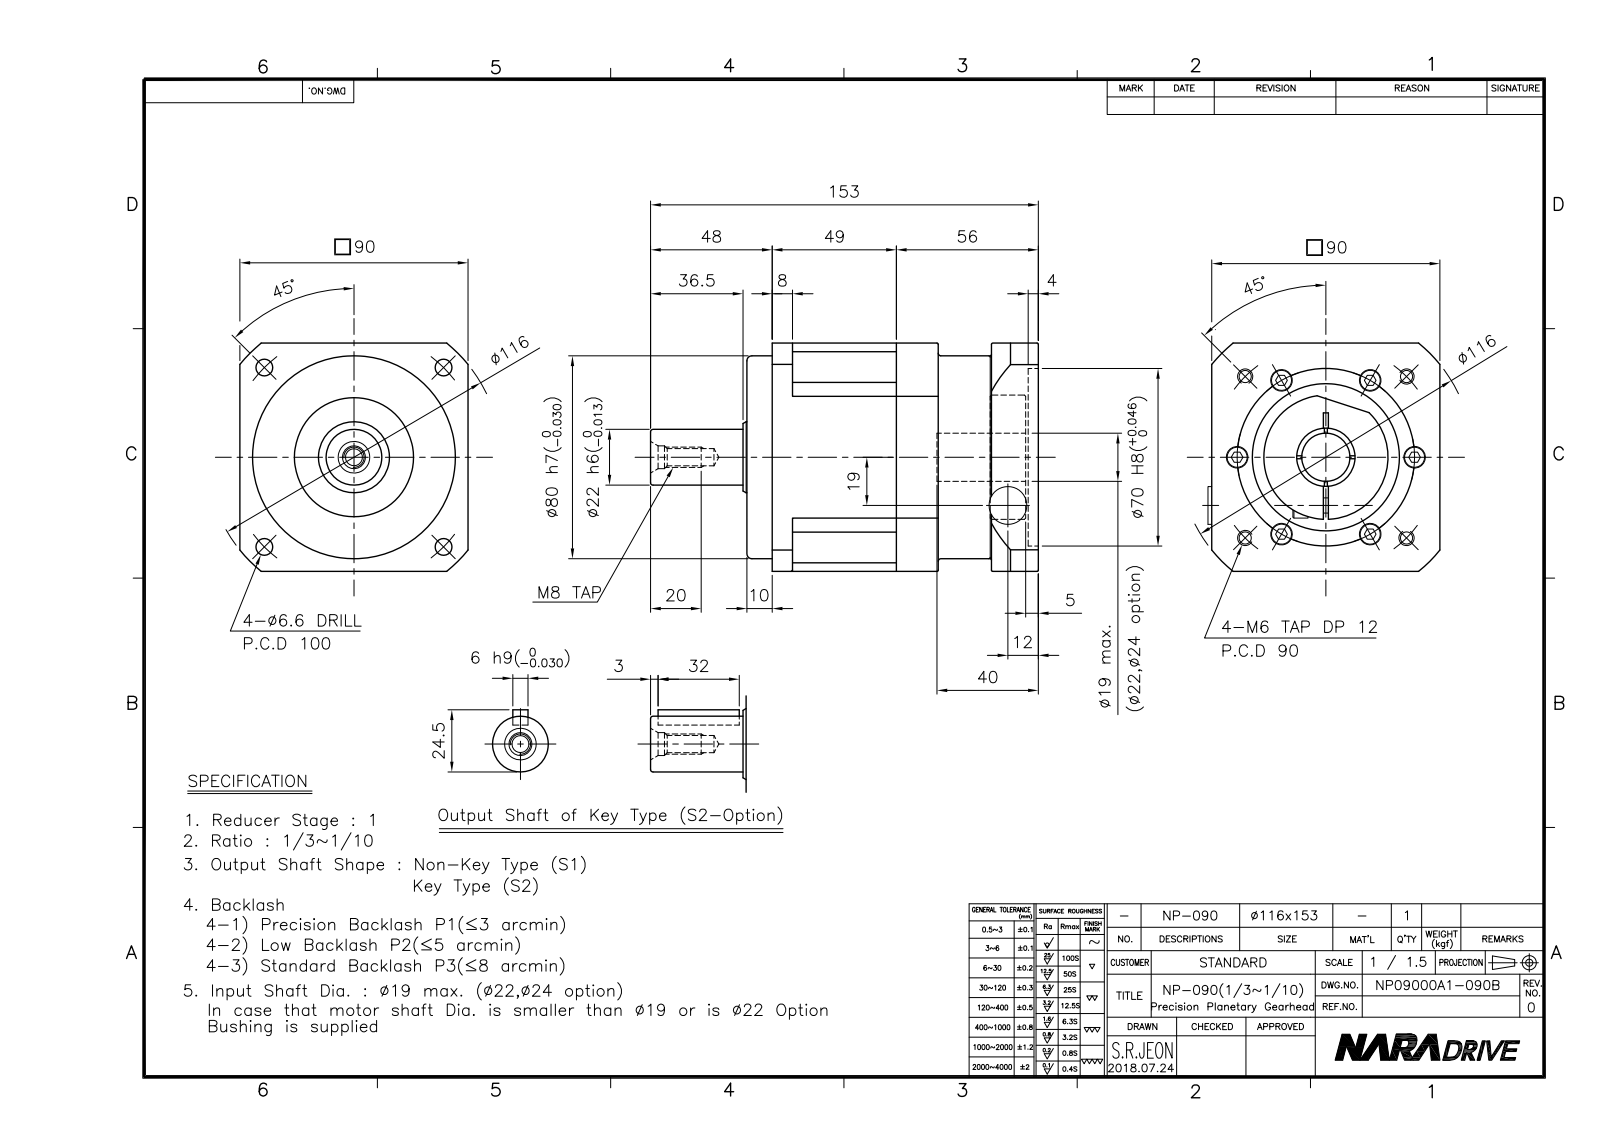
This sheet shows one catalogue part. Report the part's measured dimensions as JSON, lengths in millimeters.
{"part_name": "NP09000A1-090B-S1", "step_written_by": "Autodesk Inventor 2015 (AUTOMOTIVE_DESIGN)", "units": "millimeters", "bodies": {"solids": 2, "faces": 389, "planar": 170, "cylindrical": 123, "other": 96}, "overall_size": [153, 91.5, 90], "volume_mm3": 594358, "surface_area_mm2": 98967, "round_holes": [[9, 11], [4.13, 10], [5.5, 10], [4.92, 5], [6.6, 5], [6.65, 1], [7, 1], [8.5, 1], [19, 1], [23, 1], [28, 1], [47, 1]], "round_bosses_or_shafts": [[8.5, 6], [5, 6], [80, 1], [79, 1], [49, 1], [22, 1], [15, 1], [10, 1]], "partial_cylinders_radius": [[0.5, 16], [10, 4], [5.5, 1], [35, 1], [51, 1], [58, 1]], "face_to_face_distances": [90, 51, 8, 59, 41, 115, 64, 10, 45.5, 105], "hole_center_spacings": [35, 60.62, 14.4, 31.98, 45, 49.34, 63.64, 63.76]}
